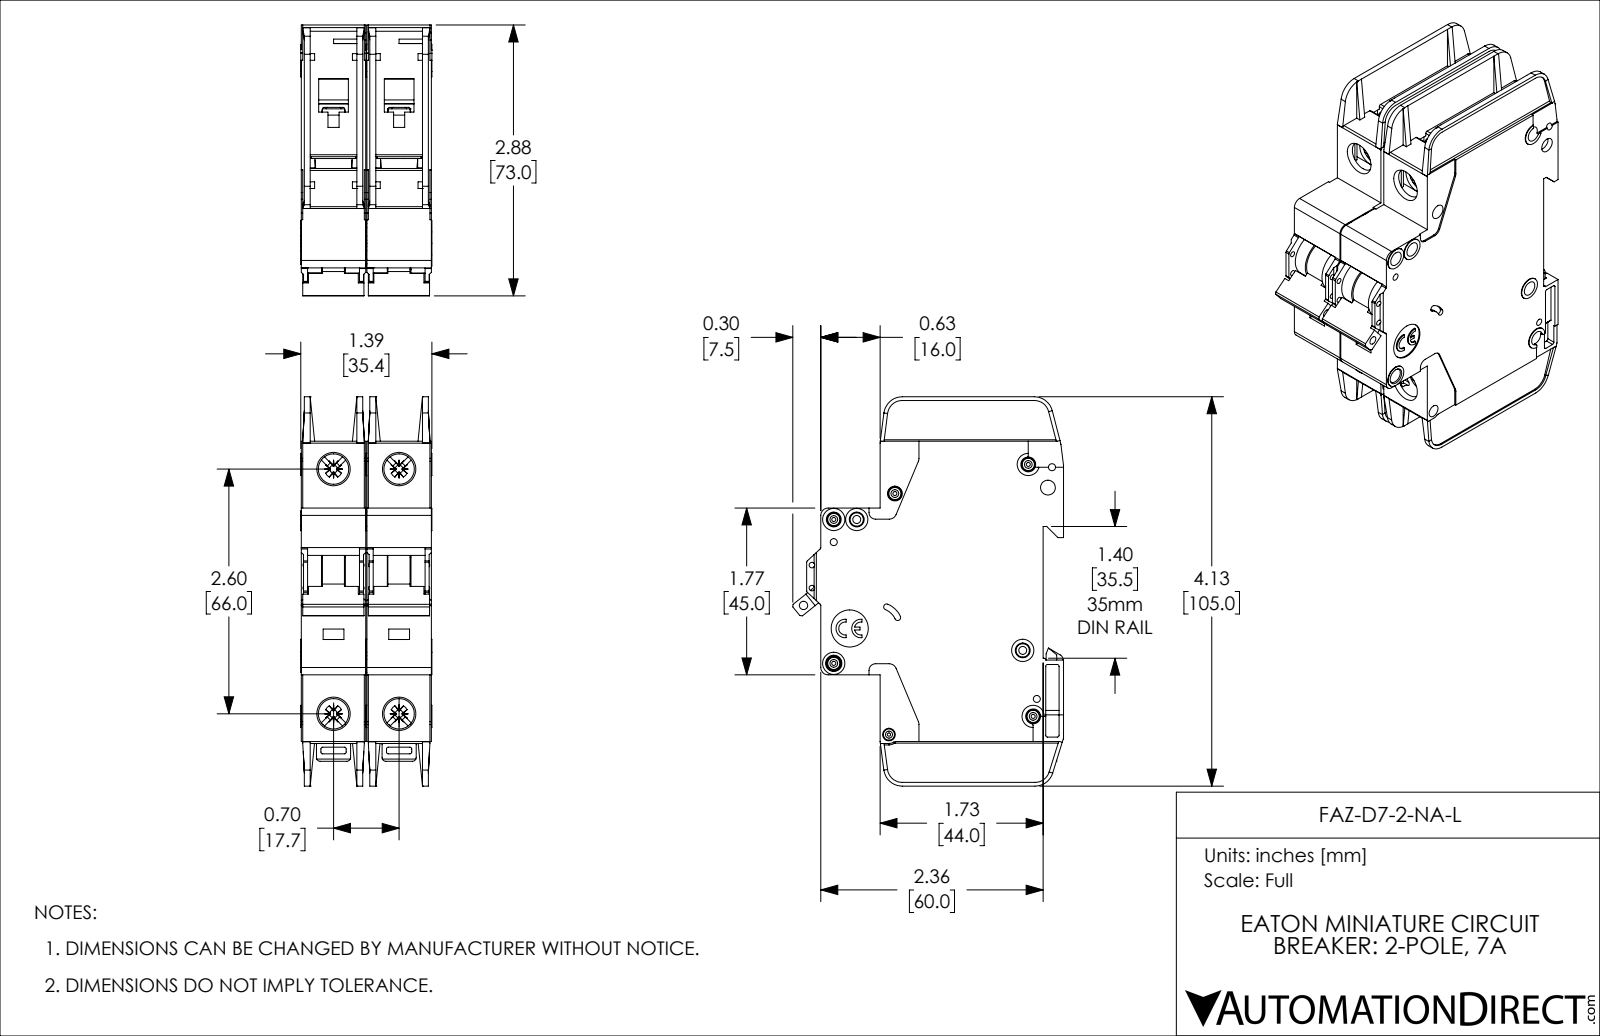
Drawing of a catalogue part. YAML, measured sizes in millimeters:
part_name: "FAZ-D7-2-NA-L"
step_written_by: "SolidWorks 2019 (AUTOMOTIVE_DESIGN)"
units: millimeters
bodies: {solids: 2, faces: 2254, planar: 1342, cylindrical: 714, other: 198}
overall_size: [105, 73.1, 35.4]
volume: 153500
surface_area: 52910
round_holes:
  - {diameter: 4, count: 8}
  - {diameter: 1.1, count: 5}
  - {diameter: 1.9, count: 4}
  - {diameter: 8.2, count: 4}
  - {diameter: 1.5, count: 2}
  - {diameter: 2.2, count: 2}
  - {diameter: 0.9, count: 1}
  - {diameter: 2.3, count: 1}
  - {diameter: 2.5, count: 1}
  - {diameter: 3.4, count: 1}
  - {diameter: 10, count: 1}
round_bosses_or_shafts:
  - {diameter: 3.3, count: 5}
  - {diameter: 6, count: 4}
  - {diameter: 3, count: 3}
  - {diameter: 2.5, count: 2}
partial_cylinders:
  - {radius: 0.5, count: 57}
  - {radius: 0.4, count: 20}
  - {radius: 1, count: 14}
  - {radius: 2, count: 10}
  - {radius: 1.1, count: 8}
  - {radius: 0.2, count: 5}
  - {radius: 5, count: 5}
  - {radius: 0.3, count: 4}
face_to_face_distances: [17.7, 1.2, 17.4, 15, 2.4, 16.2, 13.8, 35.1, 18.9, 16.5]
hole_center_spacings: [6.2, 13.6, 17.7, 22.1, 66, 68.3, 4.8, 5.1]
